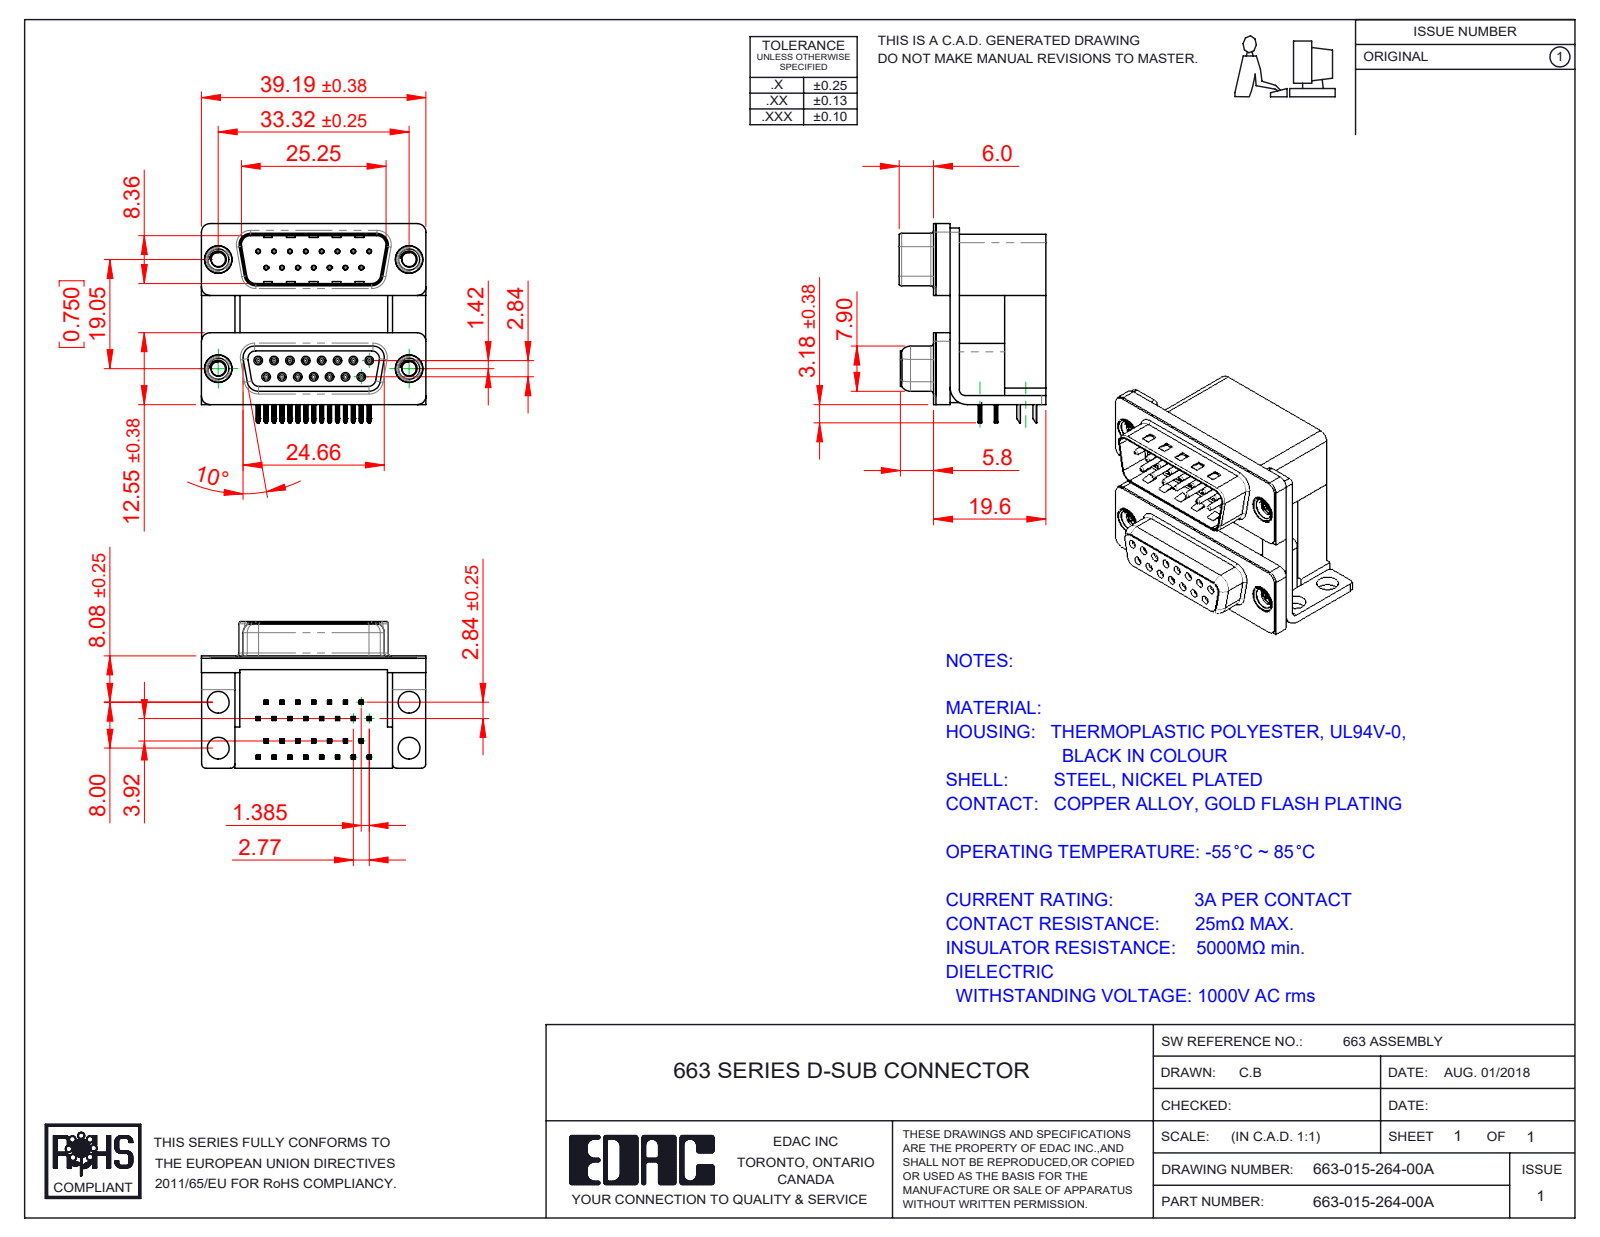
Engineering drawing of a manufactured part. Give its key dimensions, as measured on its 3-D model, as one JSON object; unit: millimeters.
{"part_name": "663 Housing Upper_15 Contacts M; 663 Contact Bottom Upper_M; 663 Threaded Rivet_M3; 663 Housing Lower_15 Contacts (+8 more)", "step_written_by": "SolidWorks 2020 (CONFIG_CONTROL_DESIGN)", "units": "millimeters", "bodies": {"solids": 41, "faces": 3916, "planar": 2015, "cylindrical": 1022, "other": 879}, "overall_size": [39.19, 34.78, 25.6], "volume_mm3": 15200, "surface_area_mm2": 16708, "round_holes": [[0.8, 30], [0.35, 15], [0.9, 15], [2.5, 4], [3.5, 4], [3.8, 4], [4, 4], [4.8, 4], [5, 4]], "round_bosses_or_shafts": [[1.2, 15], [0.75, 15], [4.9, 4], [4.75, 4], [3.9, 4]], "partial_cylinders_radius": [[0.1, 120], [0.15, 60], [0.25, 60], [0.12, 30], [0.35, 30], [1.5, 16], [0.34, 15], [0.5, 12]], "face_to_face_distances": [0.4, 19.2, 16.7, 2.5, 7.2, 12, 9.5, 10.69, 2.9, 19.6], "hole_center_spacings": [3.16, 19.25, 2.77, 19.84, 5.54, 8.31, 19.05, 20.78]}
